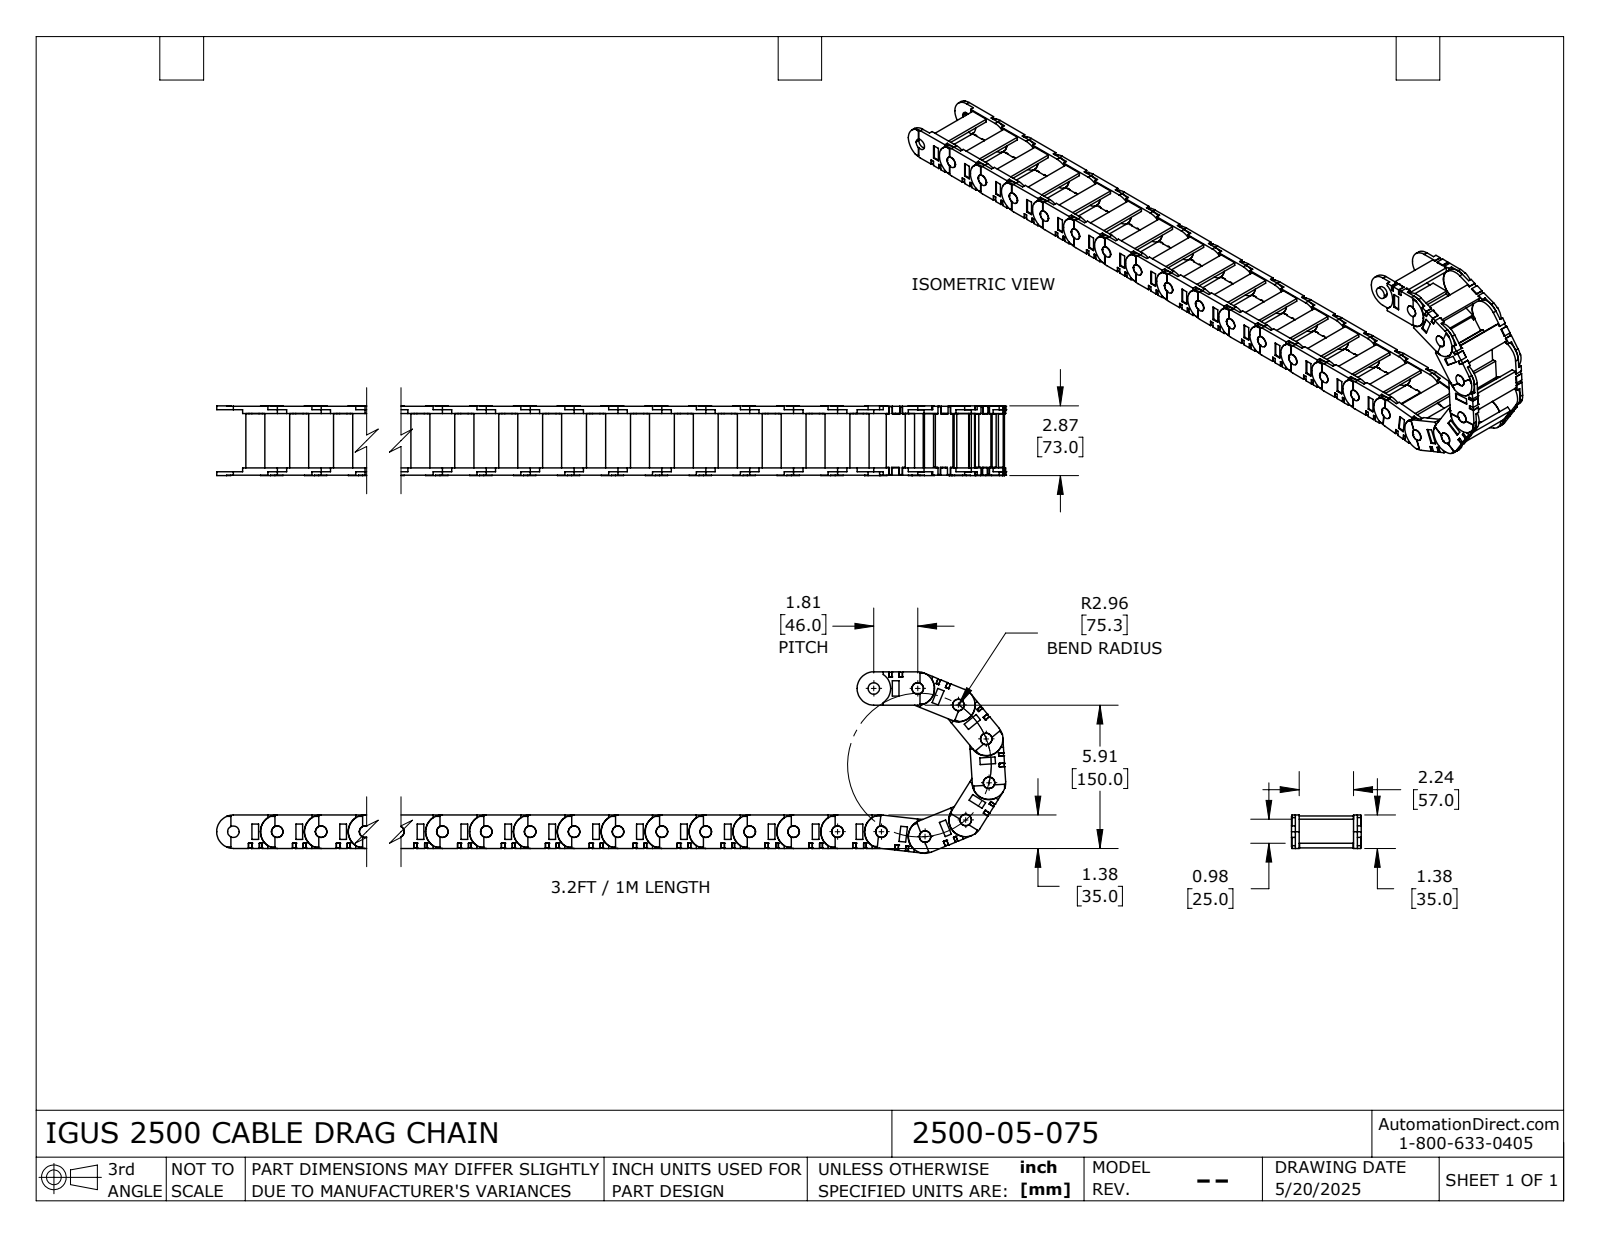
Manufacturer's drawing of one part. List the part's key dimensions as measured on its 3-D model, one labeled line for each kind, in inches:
Part name (STEP PRODUCT): 2500_05_075
STEP written by: SolidWorks 2024 (AUTOMOTIVE_DESIGN)
Units: inches
Bodies: 66 solids, 2398 faces (1870 planar, 528 cylindrical, 0 other)
Overall size (bounding box): 32.981 × 7.485 × 2.874
Volume: 45.18 in³ · Surface area: 663.9 in²
Round holes (diameter × count): ⌀0.473 ×22
Round bosses / shafts (diameter × count): ⌀0.472 ×22, ⌀1.378 ×21
Partial cylindrical surfaces — rounded edges, fillets, slot ends (radius × count): R0.697 ×23, R0.689 ×2
Main face-to-face distances: 0.157, 2.402, 2.559, 0.142, 0.299, 2.543, 2.701, 2.244, 0.197, 0.984
Hole centre spacings: 1.811, 3.622, 5.433, 7.244, 9.055, 10.866, 12.677, 14.488
